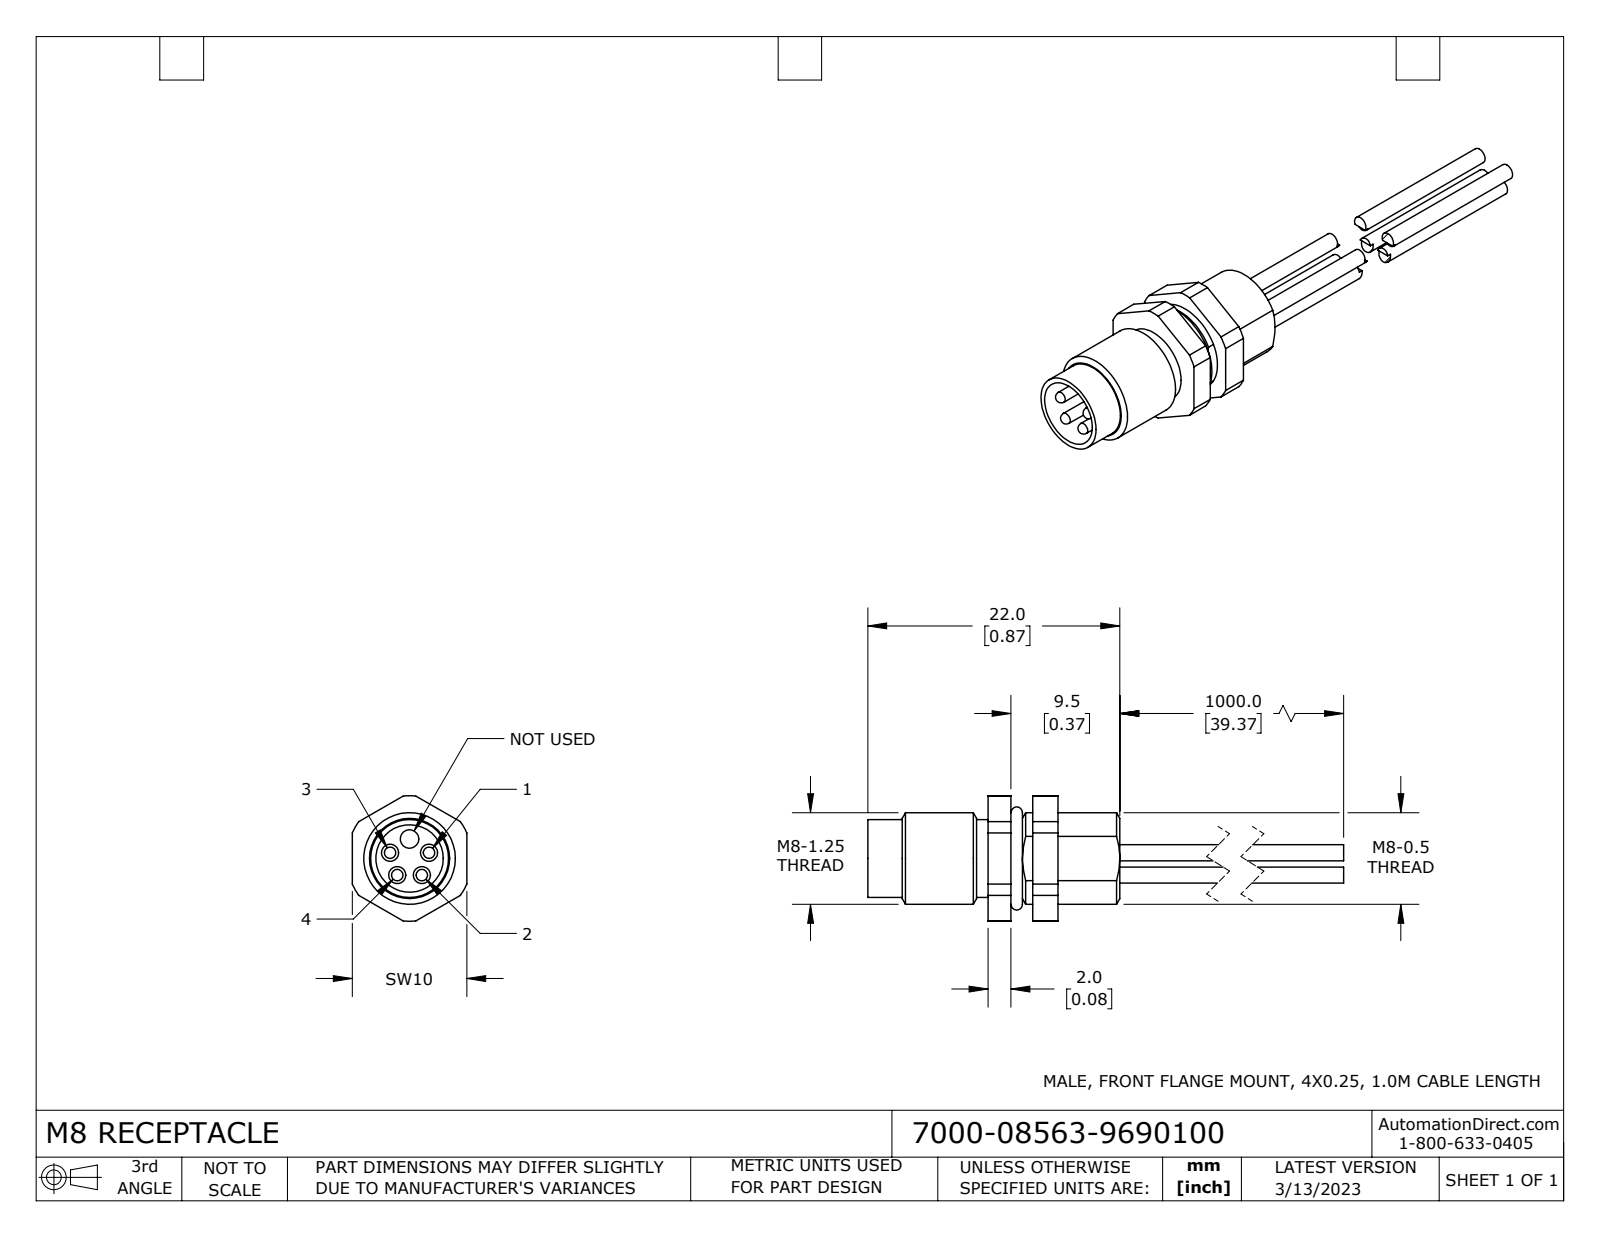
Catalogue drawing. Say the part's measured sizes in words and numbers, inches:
The part is named "7000-08563-9690100". Its 3-D file was written by "SolidWorks 2021 (CONFIG_CONTROL_DESIGN)". It is 7 solids with 112 faces: 38 planar, 54 cylindrical and 20 other. Overall it measures 4.724 by 0.431 by 0.394 inches. Its volume is 0.097 cubic inches and its surface area 4.696 square inches. Round holes: 4 of diameter 0.059, 1 of diameter 0.063, 1 of diameter 0.232, 1 of diameter 0.244. Round bosses or shafts: 4 of diameter 0.055, 4 of diameter 0.039, 1 of diameter 0.315, 1 of diameter 0.268. Partial cylindrical surfaces (rounded edges, fillets, slot ends): 1 of radius 0.216. The main face-to-face distances are 0.394, 0.079, 0.295, 0.374, 0.335, 0.276, 0.059, 0.134, 0.22, 0.087. The hole center spacings are 0.07, 0.071, 0.081, 0.082, 0.131, 0.133, 0.067, 0.084.
